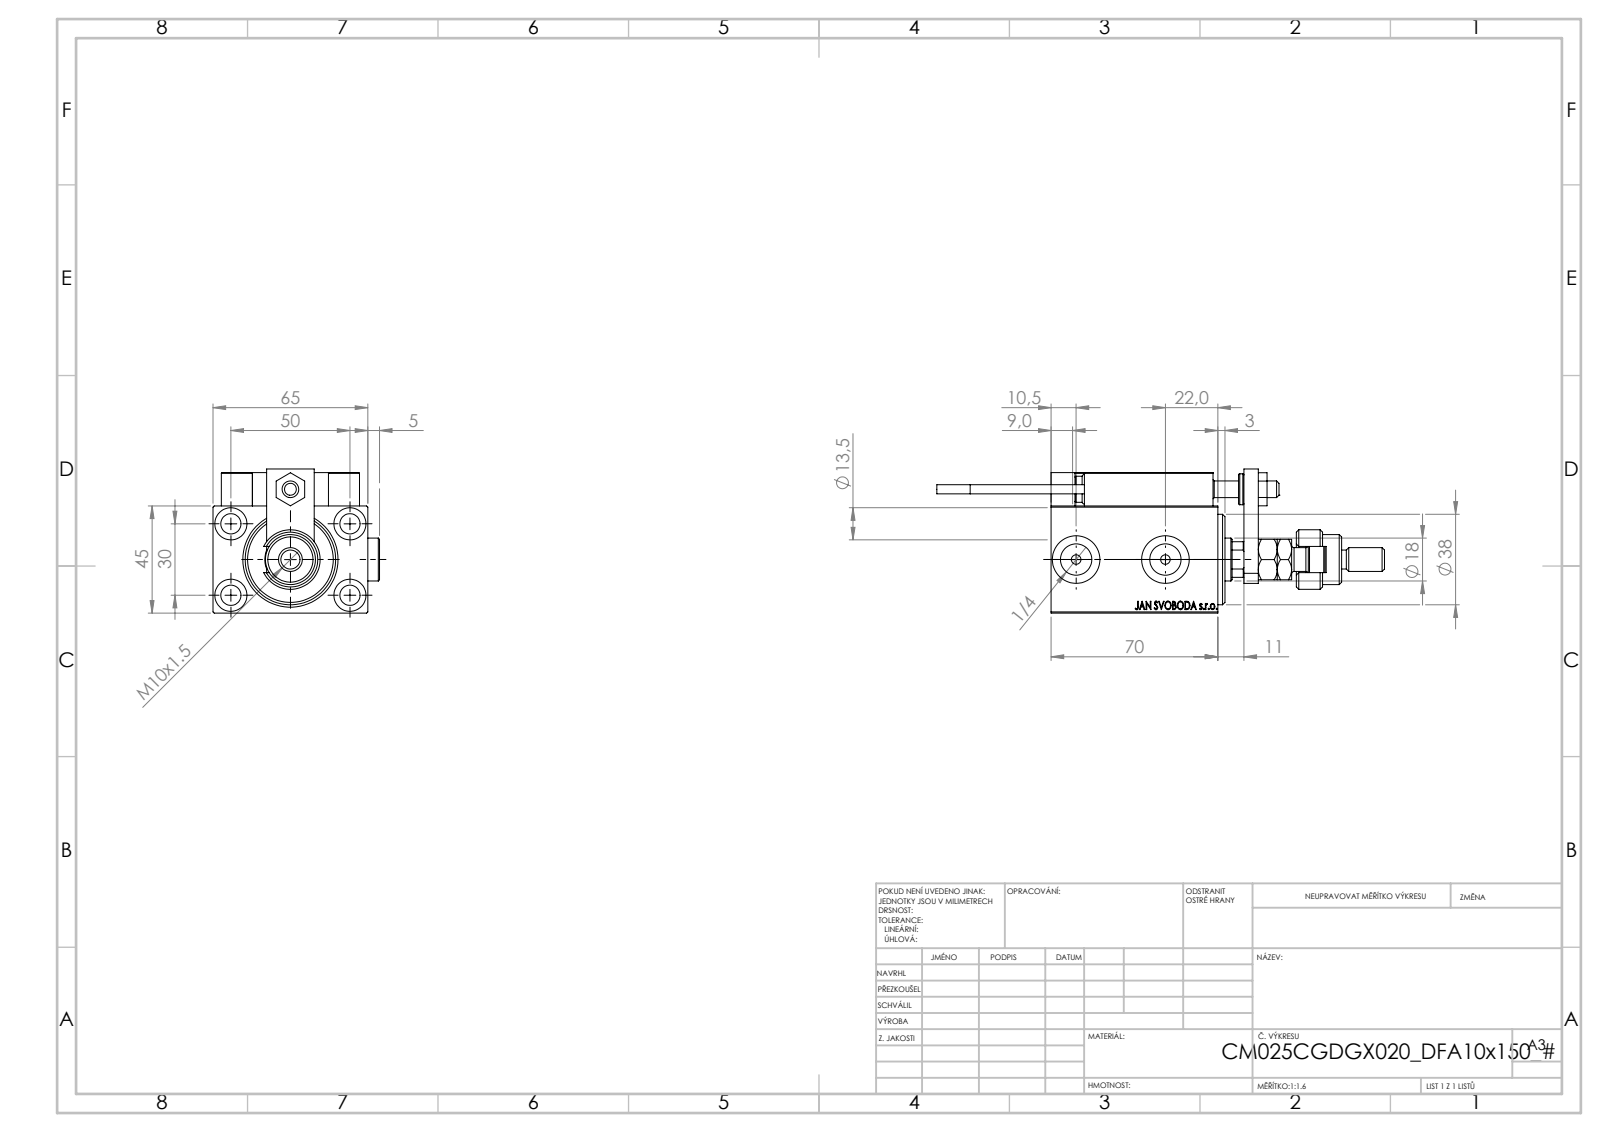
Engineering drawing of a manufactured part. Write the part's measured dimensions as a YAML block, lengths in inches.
part_name: "MFA; SWITCH DIM B,W; V450CM_C_Body; X_Y_DFA (+7 more)"
step_written_by: "SolidWorks 2019 (CONFIG_CONTROL_DESIGN)"
units: inches
bodies: {solids: 27, faces: 1421, planar: 622, cylindrical: 217, other: 582}
overall_size: [7.402, 2.752, 2.382]
volume: 14.24
surface_area: 120.2
round_holes:
  - {diameter: 0.157, count: 6}
  - {diameter: 0.315, count: 5}
  - {diameter: 0.335, count: 5}
  - {diameter: 0.126, count: 4}
  - {diameter: 0.531, count: 4}
  - {diameter: 0.197, count: 2}
  - {diameter: 0.518, count: 2}
  - {diameter: 0.787, count: 2}
  - {diameter: 0.276, count: 1}
  - {diameter: 0.571, count: 1}
  - {diameter: 0.709, count: 1}
  - {diameter: 0.846, count: 1}
round_bosses_or_shafts:
  - {diameter: 0.709, count: 2}
  - {diameter: 0.197, count: 2}
  - {diameter: 0.15, count: 2}
  - {diameter: 0.984, count: 1}
  - {diameter: 0.827, count: 1}
  - {diameter: 0.63, count: 1}
  - {diameter: 0.512, count: 1}
  - {diameter: 0.433, count: 1}
partial_cylinders:
  - {radius: 0.012, count: 30}
  - {radius: 0.118, count: 2}
  - {radius: 0.217, count: 1}
  - {radius: 0.335, count: 1}
  - {radius: 0.344, count: 1}
face_to_face_distances: [1.772, 2.323, 0.551, 2.559, 0.236, 0.197, 0.118, 0.748, 0.276, 0.512]
hole_center_spacings: [1.148, 0.448, 0.787, 0.87, 1.138, 1.165, 1.169, 1.181]
